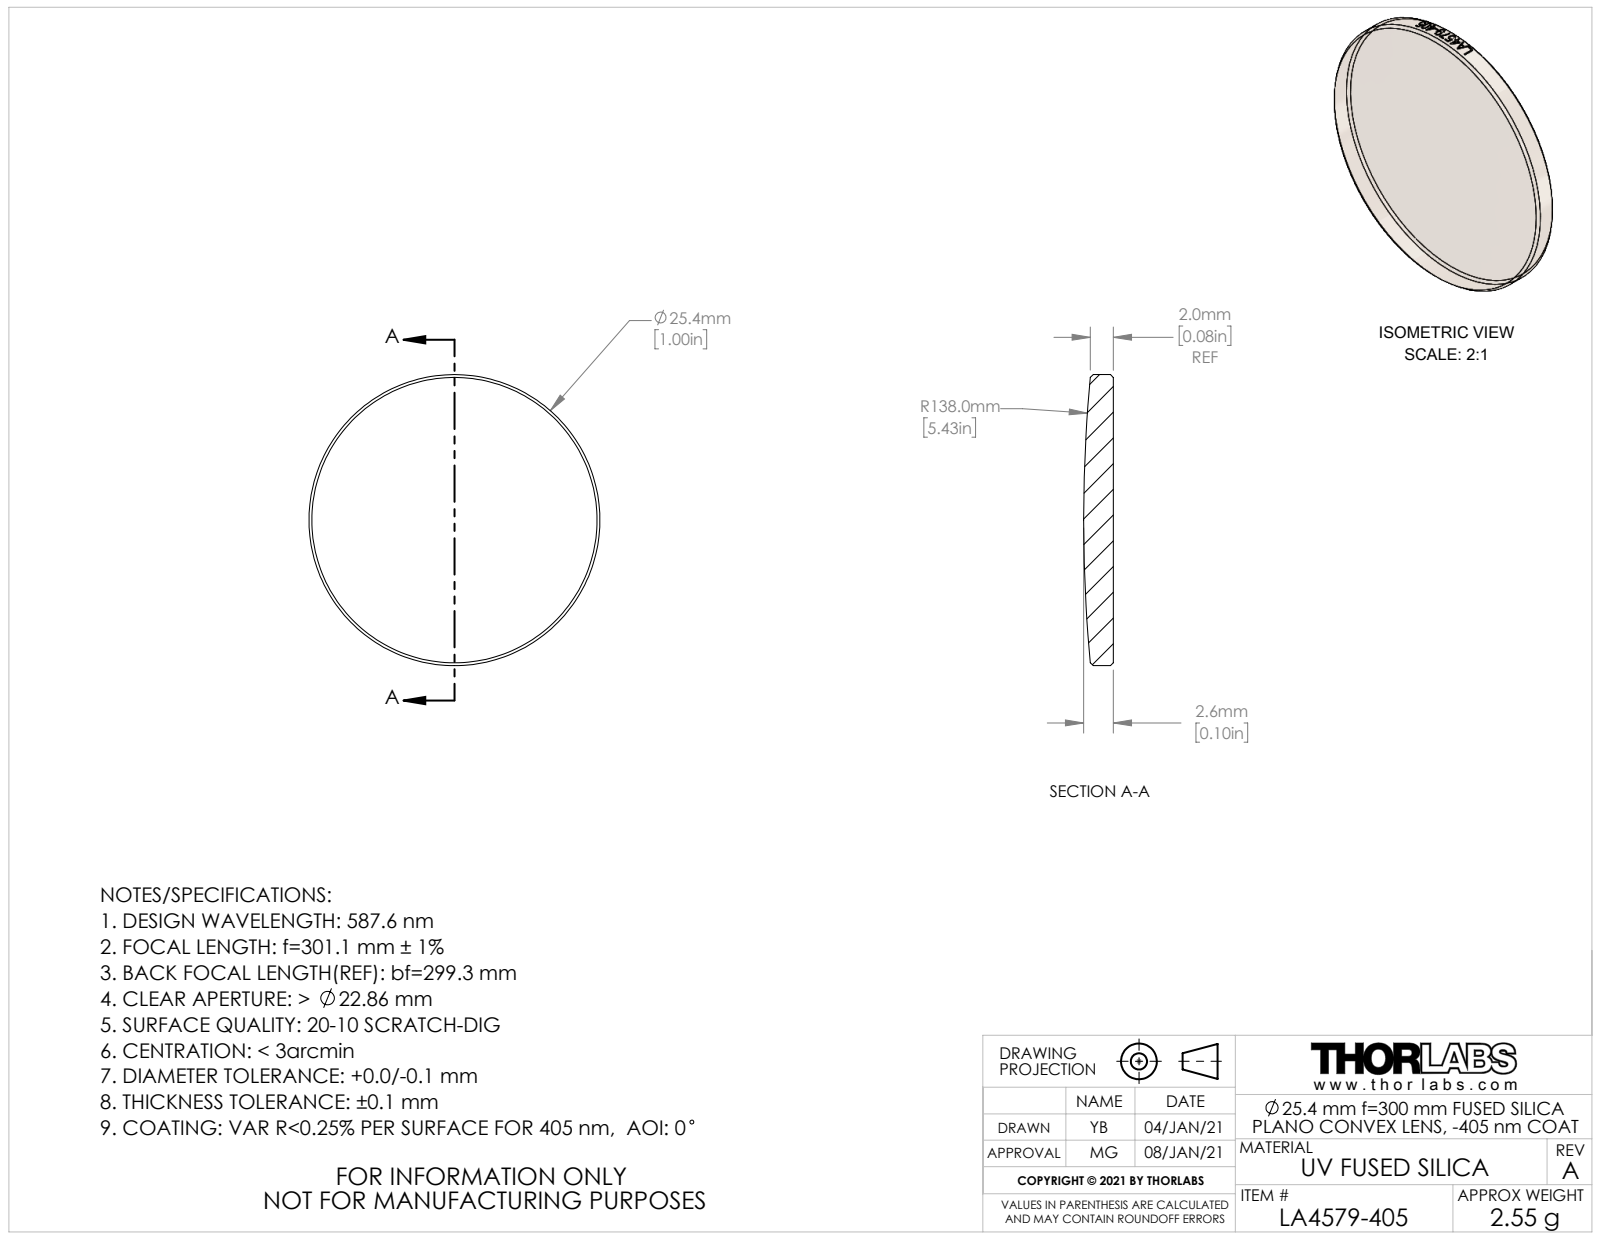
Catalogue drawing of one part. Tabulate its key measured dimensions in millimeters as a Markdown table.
| quantity | value |
| --- | --- |
| part name | CTN016818-E0W; CTN016838 |
| STEP written by | SolidWorks 2018 (AUTOMOTIVE_DESIGN) |
| units | millimeters |
| bodies | 1 solid, 27 faces (1 planar, 20 cylindrical, 6 other) |
| overall size | 25.4 × 25.4 × 2.6 |
| volume | 1 200 mm³ |
| surface area | 1 152 mm² |
| round bosses / shafts (diameter × count) | 25.4 × 1 |
